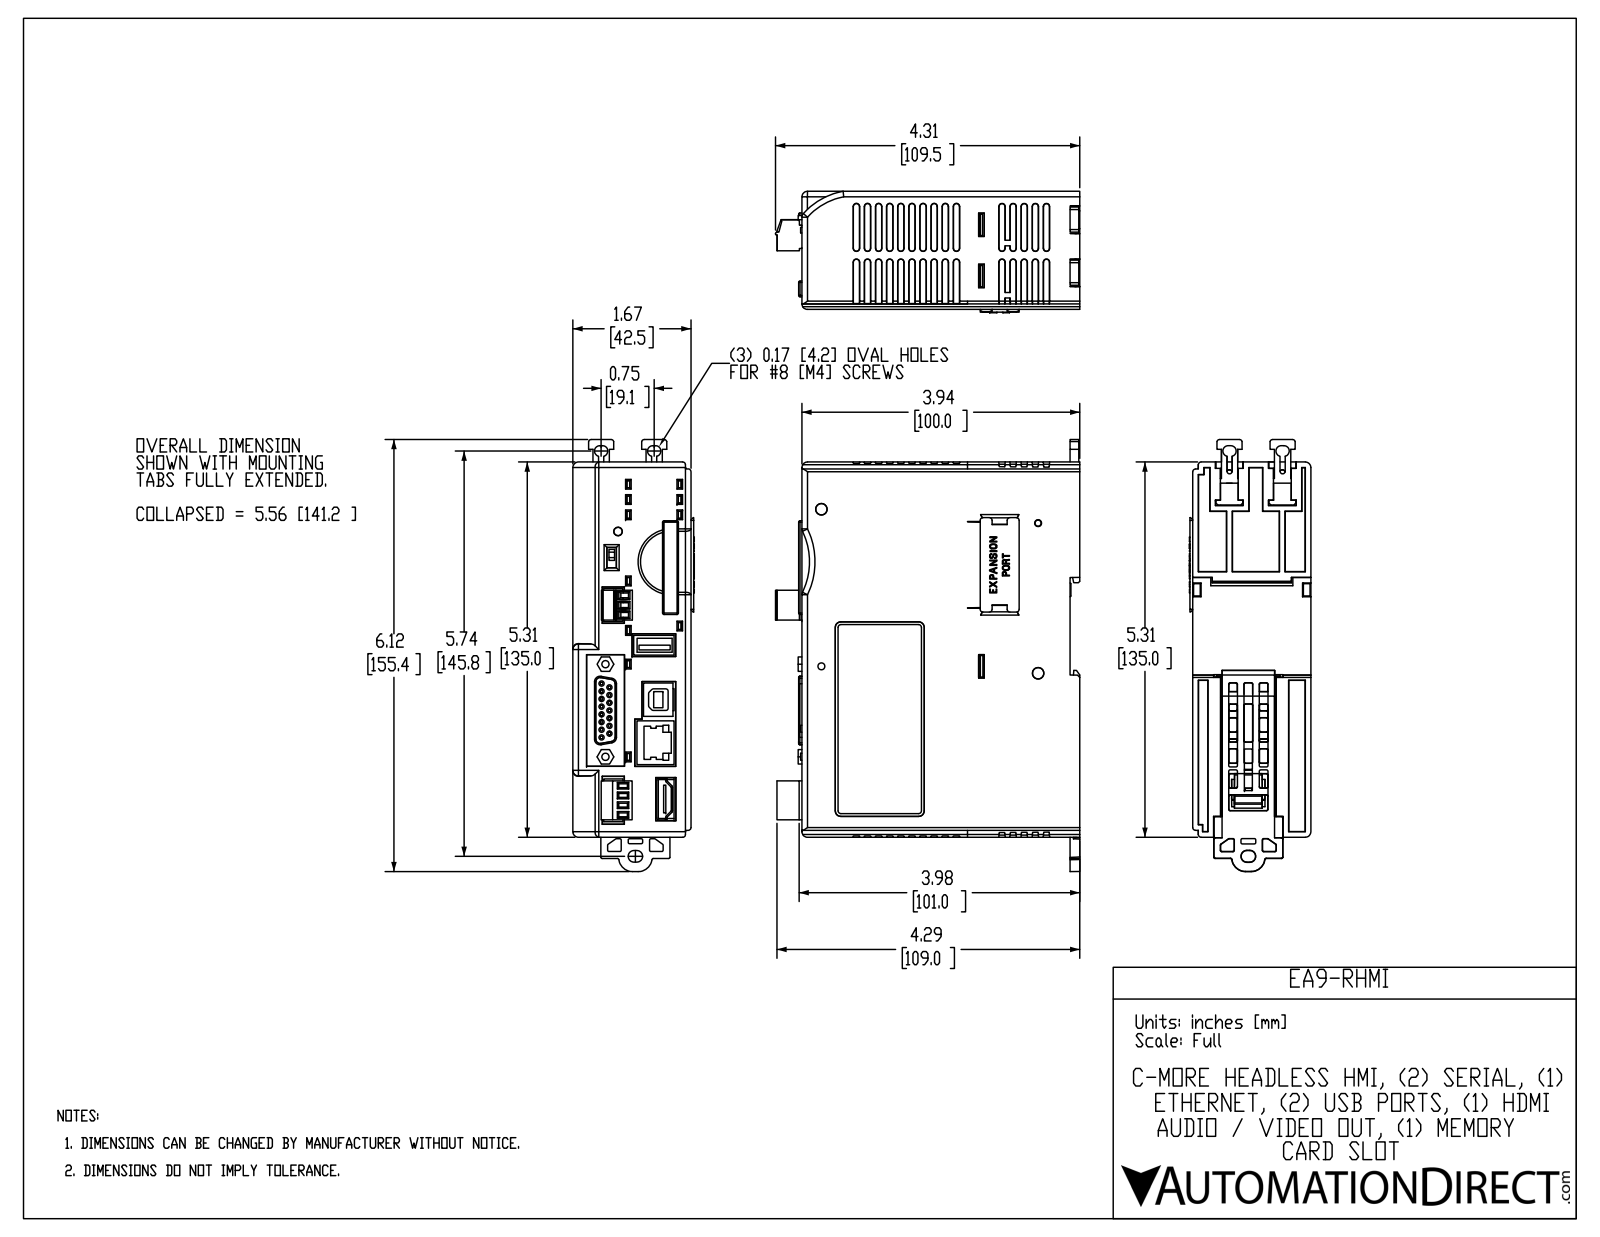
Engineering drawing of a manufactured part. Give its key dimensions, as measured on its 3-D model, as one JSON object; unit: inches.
{"part_name": "EA9_RHMI", "step_written_by": "SolidWorks 2017 (AUTOMOTIVE_DESIGN)", "units": "inches", "bodies": {"solids": 1, "faces": 2979, "planar": 2268, "cylindrical": 316, "other": 395}, "overall_size": [5.561, 4.311, 1.72], "volume_in3": 33.55, "surface_area_in2": 101.1, "round_holes": [[0.039, 19], [0.11, 4], [0.114, 3], [0.098, 2], [0.102, 2]], "round_bosses_or_shafts": [[0.102, 4], [0.031, 4], [0.11, 3], [0.018, 1]], "partial_cylinders_radius": [[0.02, 90], [0.039, 29], [0.079, 17], [0.012, 14], [0.006, 10], [0.031, 10], [0.008, 8], [0.028, 8]], "face_to_face_distances": [1.673, 0.02, 3.799, 0.079, 5.315, 0.138, 3.937, 1.665, 1.654, 1.646], "hole_center_spacings": [0.124, 0.109, 0.218, 0.327, 0.138, 0.436, 0.198, 0.198]}
